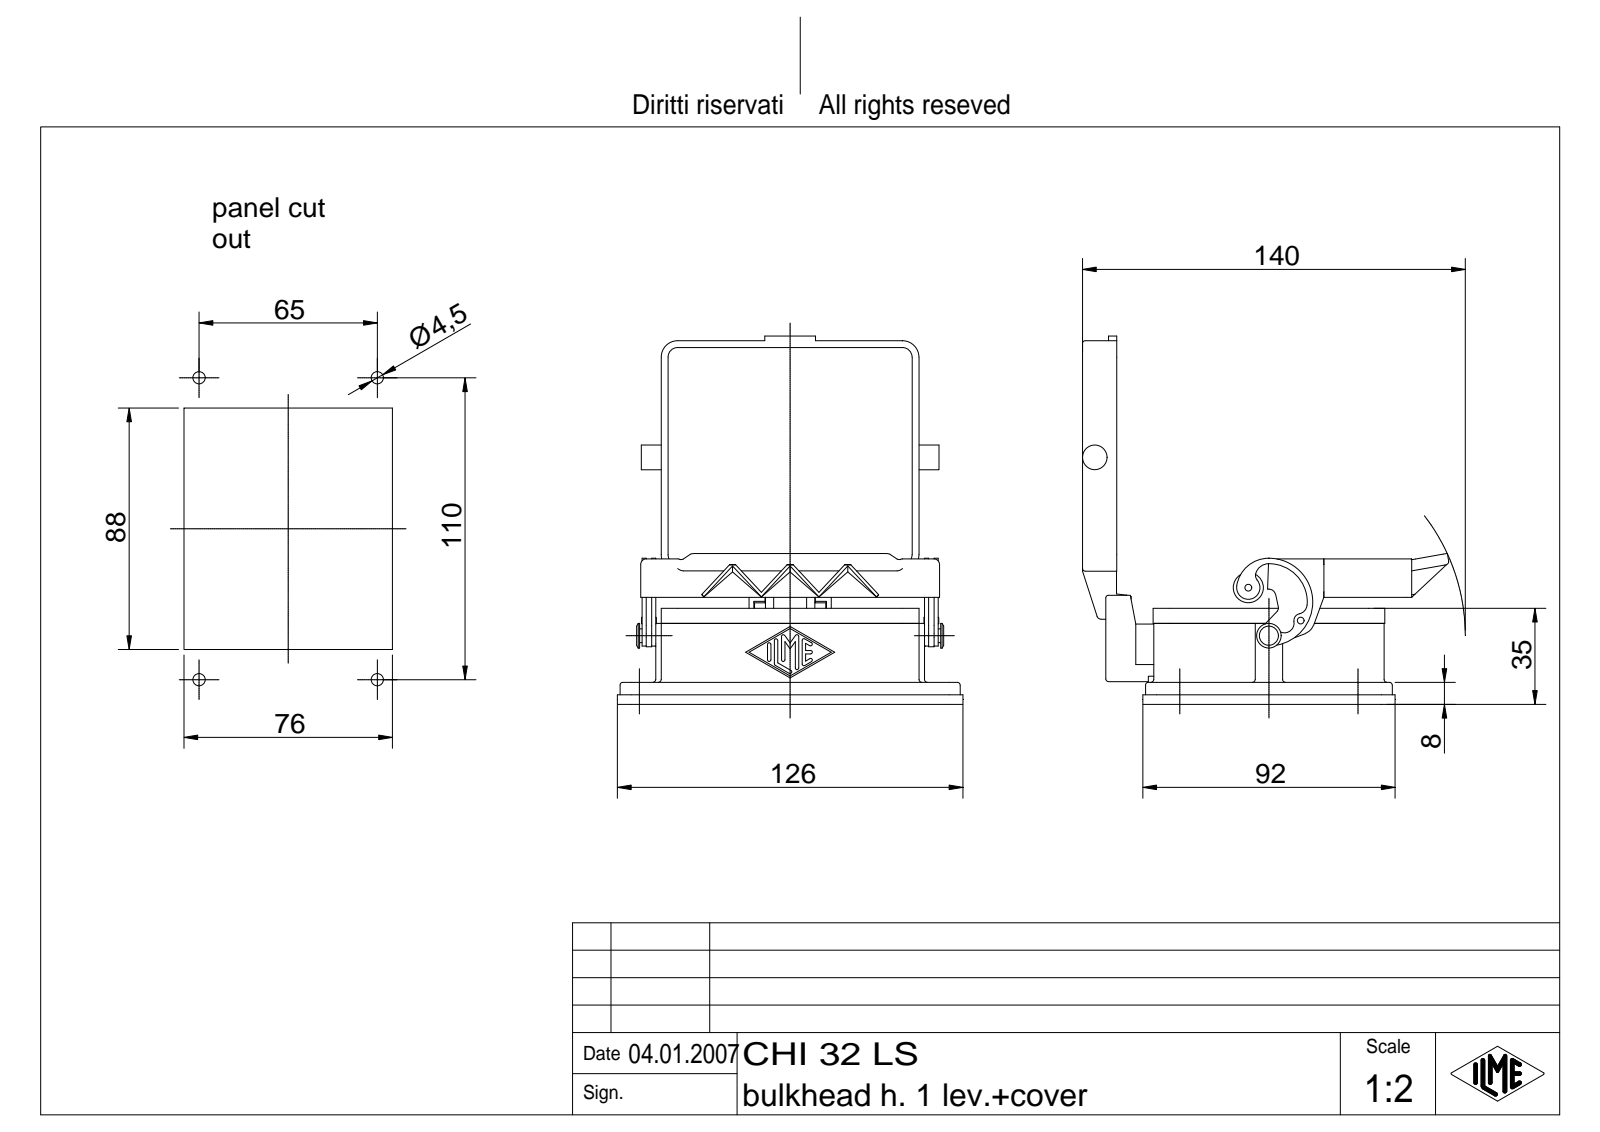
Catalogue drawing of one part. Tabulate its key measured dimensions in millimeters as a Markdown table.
| quantity | value |
| --- | --- |
| part name | CHI 32 LS |
| STEP written by | Autodesk Inventor 7 (AUTOMOTIVE_DESIGN) |
| units | millimeters |
| bodies | 6 solids, 702 faces (255 planar, 233 cylindrical, 214 other) |
| overall size | 134.2 × 133.59 × 126 |
| volume | 138 630 mm³ |
| surface area | 81 725 mm² |
| round holes (diameter × count) | 4.4 × 4, 4.5 × 4, 2 × 1, 4 × 1 |
| round bosses / shafts (diameter × count) | 9 × 2, 5 × 2, 11 × 1, 7 × 1, 4 × 1, 3 × 1, 2.5 × 1 |
| partial cylindrical surfaces (radius × count) | 1 × 30, 0.62 × 14, 2 × 12, 6 × 12, 2.5 × 7, 1.5 × 6, 3.5 × 6, 5 × 6 |
| main face-to-face distances | 3.5, 3, 91, 4, 107, 29.5, 21.5, 81, 84, 8 |
| hole center spacings | 65, 110, 127.77 |
